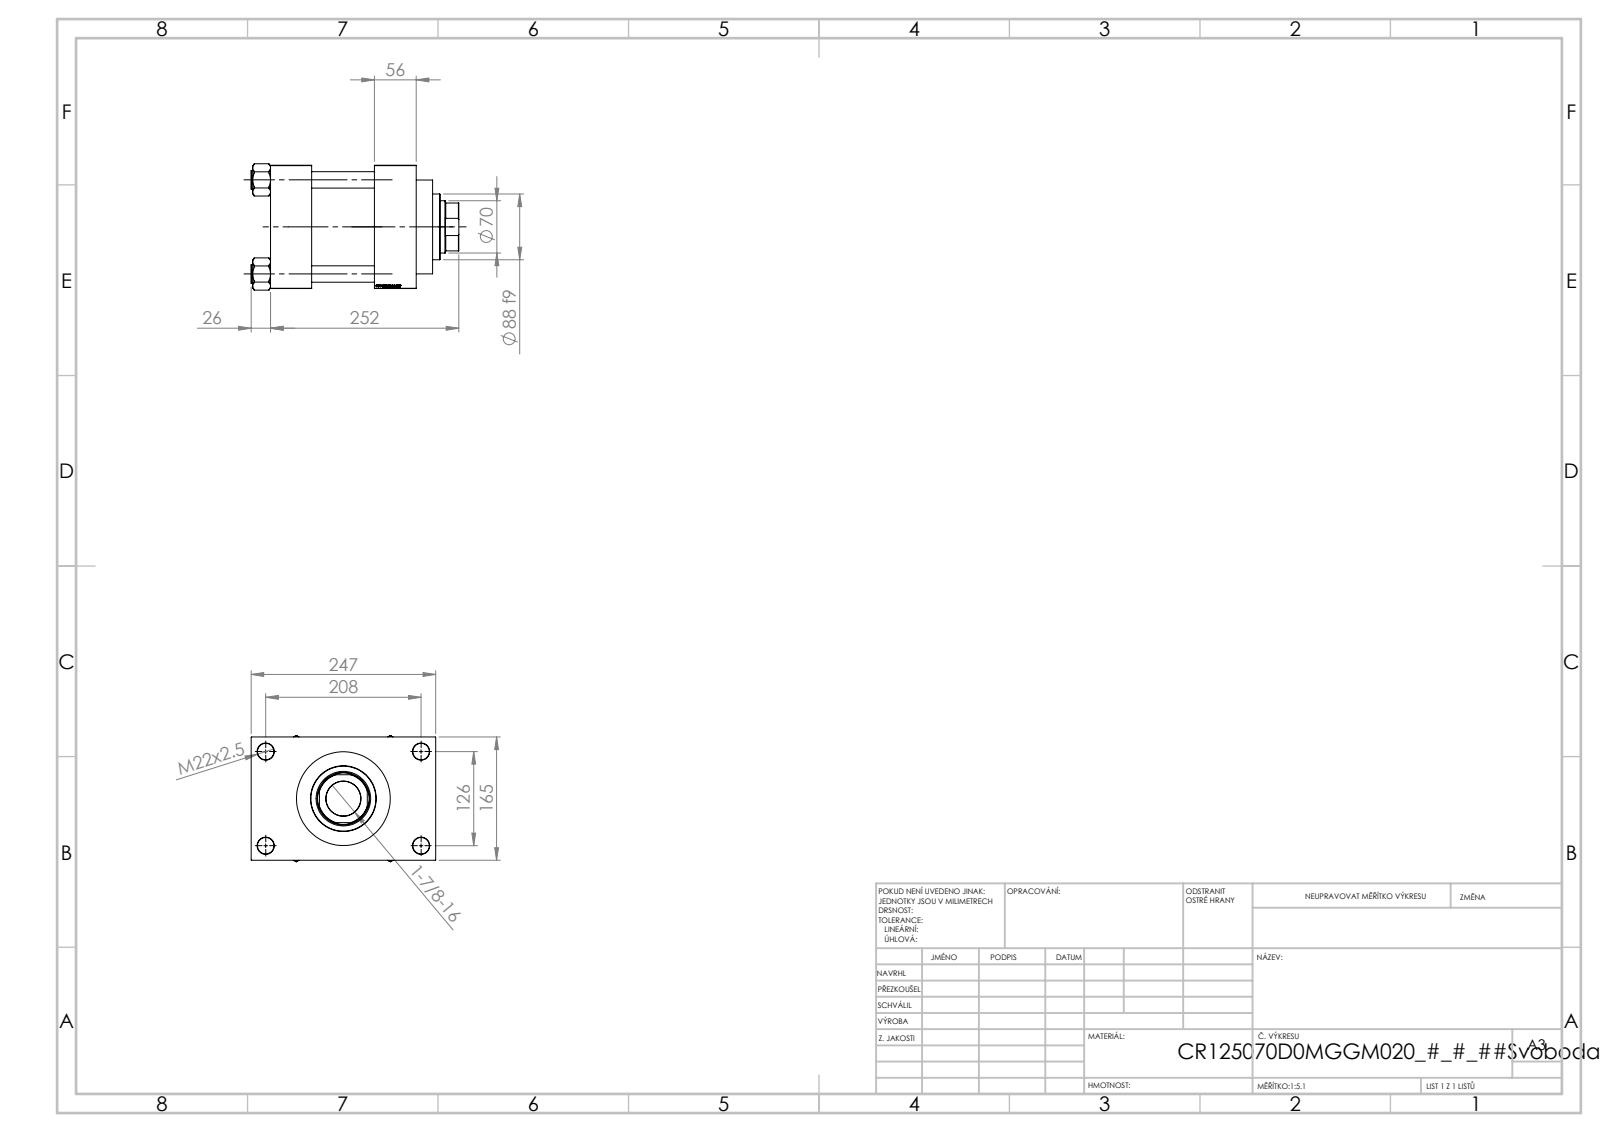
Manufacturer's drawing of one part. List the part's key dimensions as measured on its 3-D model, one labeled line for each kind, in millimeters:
Part name (STEP PRODUCT): V215CR_VCP_D; NUT_M5_D; V215_VC_A; V215CR_D_TYCINKA (+1 more)
STEP written by: SolidWorks 2019 (CONFIG_CONTROL_DESIGN)
Units: millimetres
Bodies: 11 solids, 1149 faces (544 planar, 87 cylindrical, 518 other)
Overall size (bounding box): 278 × 247 × 169.14
Volume: 5 046 000 mm³ · Surface area: 538 001 mm²
Round holes (diameter × count): ⌀22 ×8, ⌀7 ×2, ⌀32.24 ×2, ⌀45 ×2, ⌀46.5 ×1, ⌀70 ×1, ⌀73 ×1, ⌀96 ×1, ⌀125 ×1, ⌀125.5 ×1
Round bosses / shafts (diameter × count): ⌀25 ×4, ⌀131 ×1, ⌀88 ×1
Partial cylindrical surfaces — rounded edges, fillets, slot ends (radius × count): R34 ×1
Main face-to-face distances: 165, 84, 55, 139, 195, 140, 56, 41, 206, 173.74
Hole centre spacings: 41.05, 89.02, 121.59, 125.9, 132.47, 166.95, 209.13, 126
